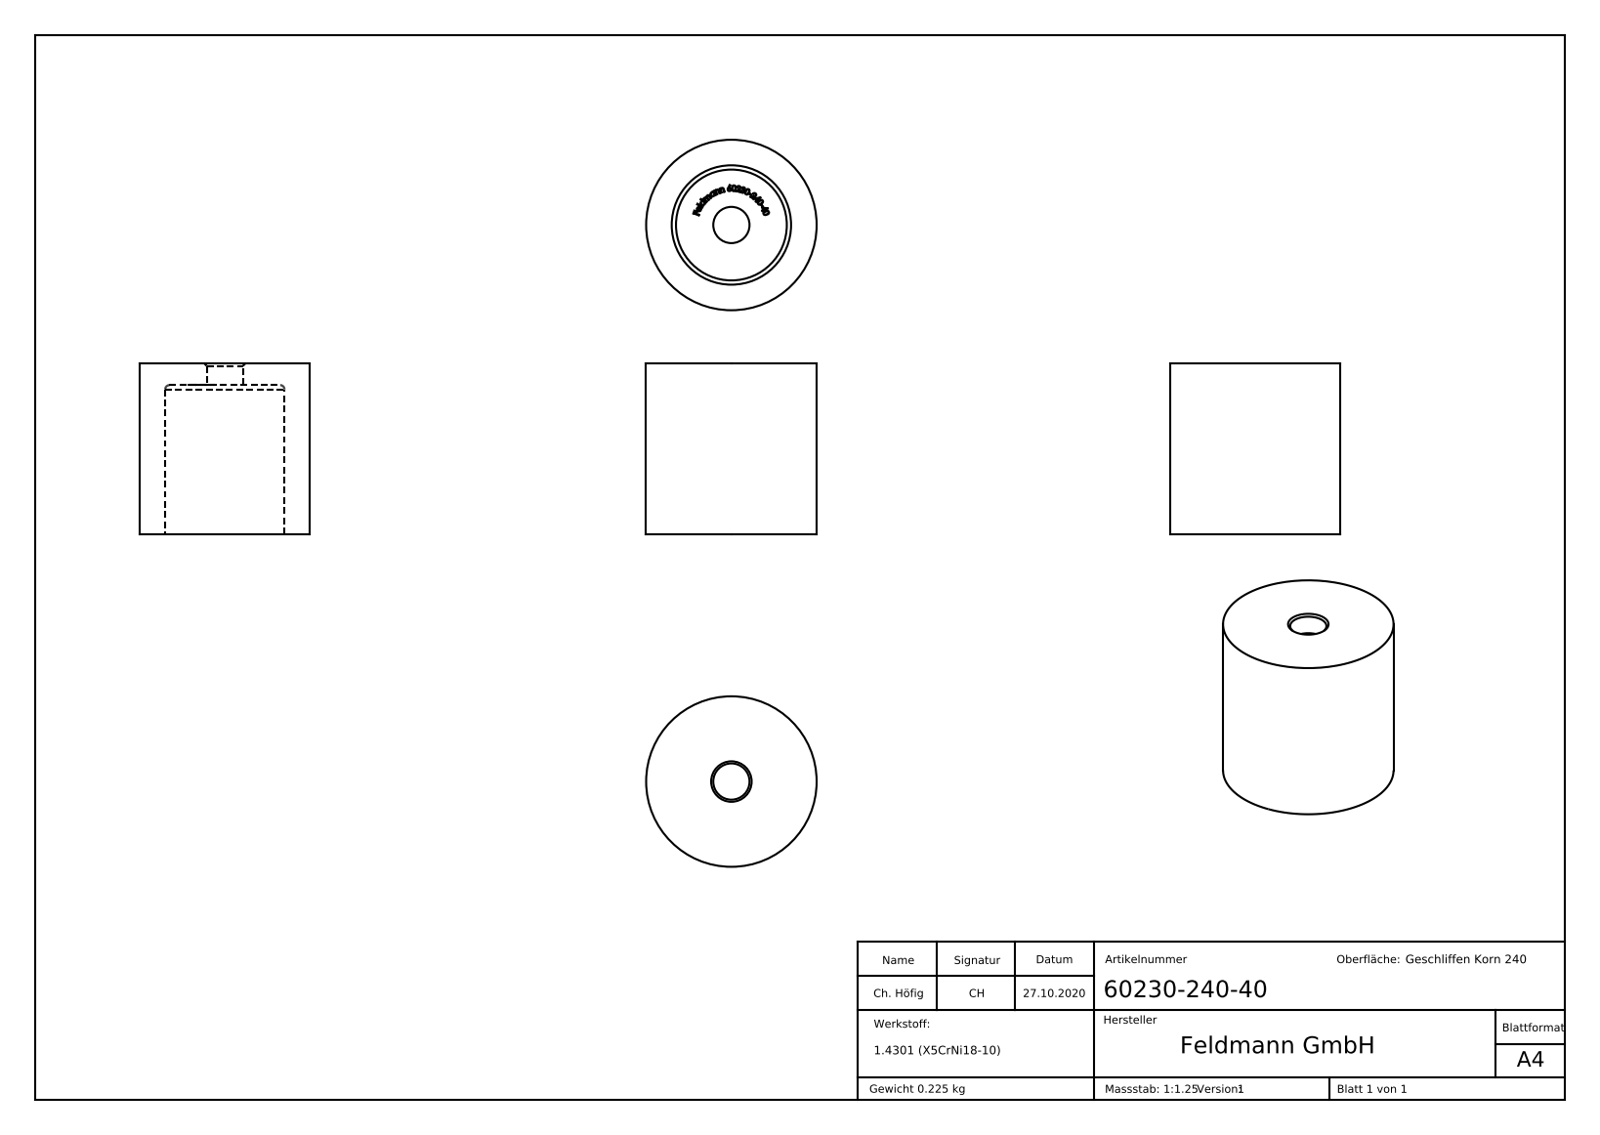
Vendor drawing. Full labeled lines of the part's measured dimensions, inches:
Part name (STEP PRODUCT): 60230-240-40
STEP written by: SolidWorks 2018 (CONFIG_CONTROL_DESIGN)
Units: inches
Bodies: 1 solid, 268 faces (139 planar, 6 cylindrical, 123 other)
Overall size (bounding box): 1.575 × 1.575 × 1.575
Volume: 1.736 in³ · Surface area: 16.44 in²
Round holes (diameter × count): ⌀0.335 ×1, ⌀1.102 ×1
Round bosses / shafts (diameter × count): ⌀1.575 ×1
Main face-to-face distances: 1.575, 1.378, 0.197, 1.382, 0.193, 0.021, 0.026, 0.026, 0.028, 0.031
